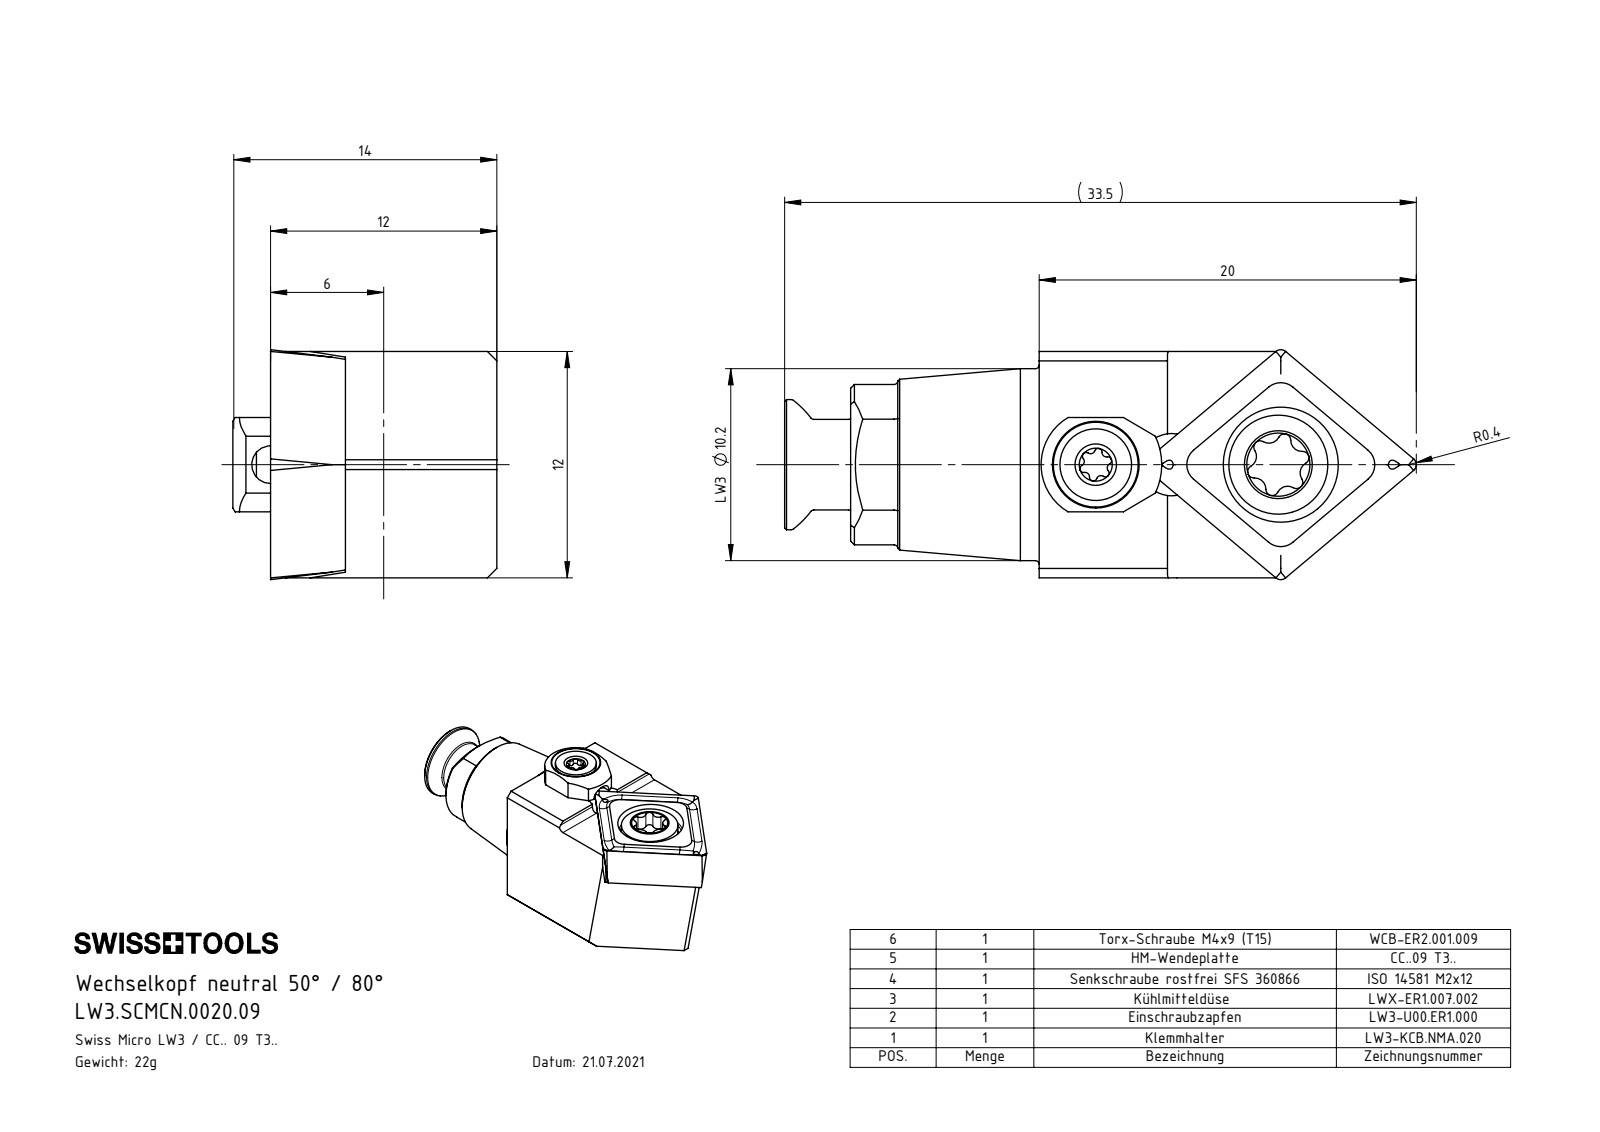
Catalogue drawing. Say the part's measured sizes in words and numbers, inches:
The part is named "LW3-U00.ER1.000_B; WCB-ER2.001.009_A; ISO 14581 - M2x12; CCMT09T304 (+3 more)". Its 3-D file was written by "SolidWorks 2022 (CONFIG_CONTROL_DESIGN)". It is 6 solids with 258 faces: 71 planar, 78 cylindrical and 109 other. Overall it measures 1.315 by 0.551 by 0.48 inches. Its volume is 0.173 cubic inches and its surface area 3.996 square inches. Round holes: 2 of diameter 0.13, 1 of diameter 0.063, 1 of diameter 0.079, 1 of diameter 0.098, 1 of diameter 0.118, 1 of diameter 0.173, 1 of diameter 0.217, 1 of diameter 0.24. Round bosses or shafts: 1 of diameter 0.401, 1 of diameter 0.272, 1 of diameter 0.236, 1 of diameter 0.207, 1 of diameter 0.197, 1 of diameter 0.189, 1 of diameter 0.157, 1 of diameter 0.15. Partial cylindrical surfaces (rounded edges, fillets, slot ends): 8 of radius 0.008, 6 of radius 0.009, 6 of radius 0.013, 6 of radius 0.023, 1 of radius 0.02, 1 of radius 0.039, 1 of radius 0.114, 1 of radius 0.138. The main face-to-face distances are 0.472, 0.316, 0.156, 0.079, 0.098, 0.528, 0.441, 0.125, 0.031, 0.449. The hole center spacings are 0.158, 0.223, 0.228, 0.381, 0.386.
